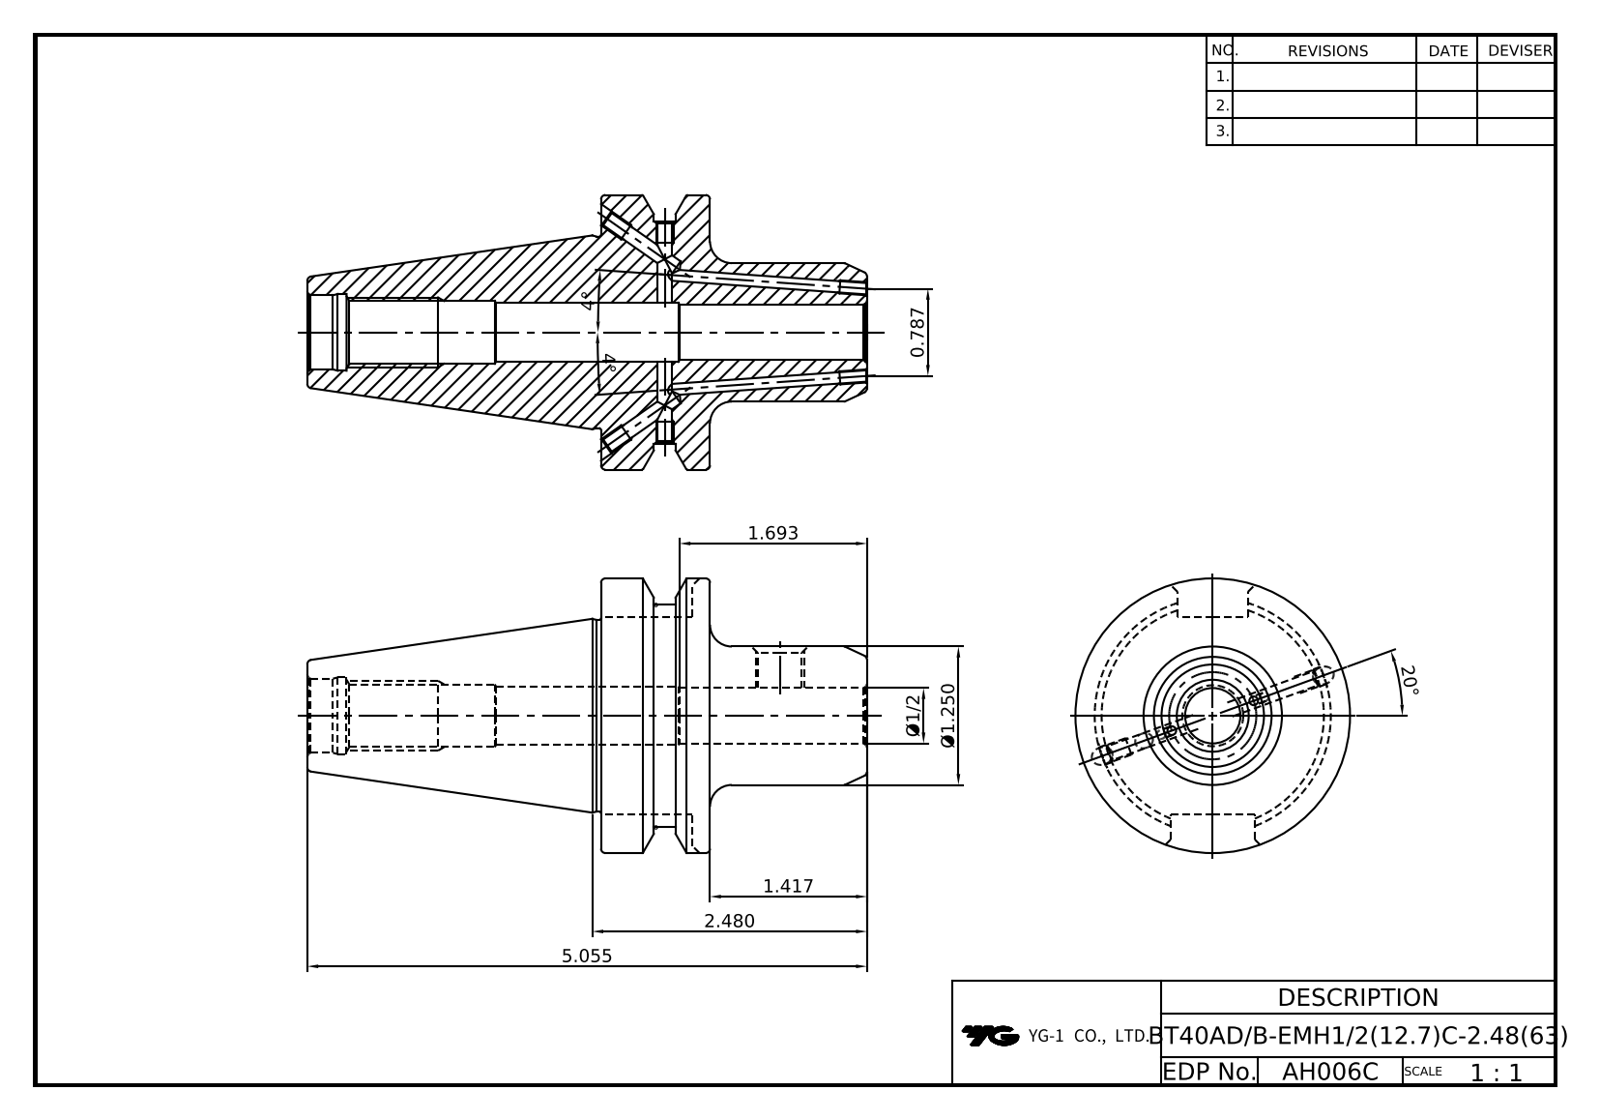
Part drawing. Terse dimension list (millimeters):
name: BT40ADB_EMH12_7C_63
written by: CREO PARAMETRIC BY PTC INC, 2018100 (CONFIG_CONTROL_DESIGN)
unit: mm
bodies: 1 solid, 149 faces (32 planar, 66 cylindrical, 51 other)
size: 128.4 × 63 × 63
volume: 140 916 mm³; area: 30 740 mm²
holes: 5× ⌀4, 3× ⌀3.4, 2× ⌀2.5, 2× ⌀3, 2× ⌀4.2, 1× ⌀9.92, 1× ⌀11.11, 1× ⌀12.7, 1× ⌀13.5, 1× ⌀14, 1× ⌀16, 1× ⌀17
bosses: 1× ⌀63, 1× ⌀51, 1× ⌀44, 1× ⌀31.75
rounds: 1× R8.05
face distances: 25, 61, 36, 45.2, 17.1, 7.9, 43.9, 12.1, 5, 12.9
